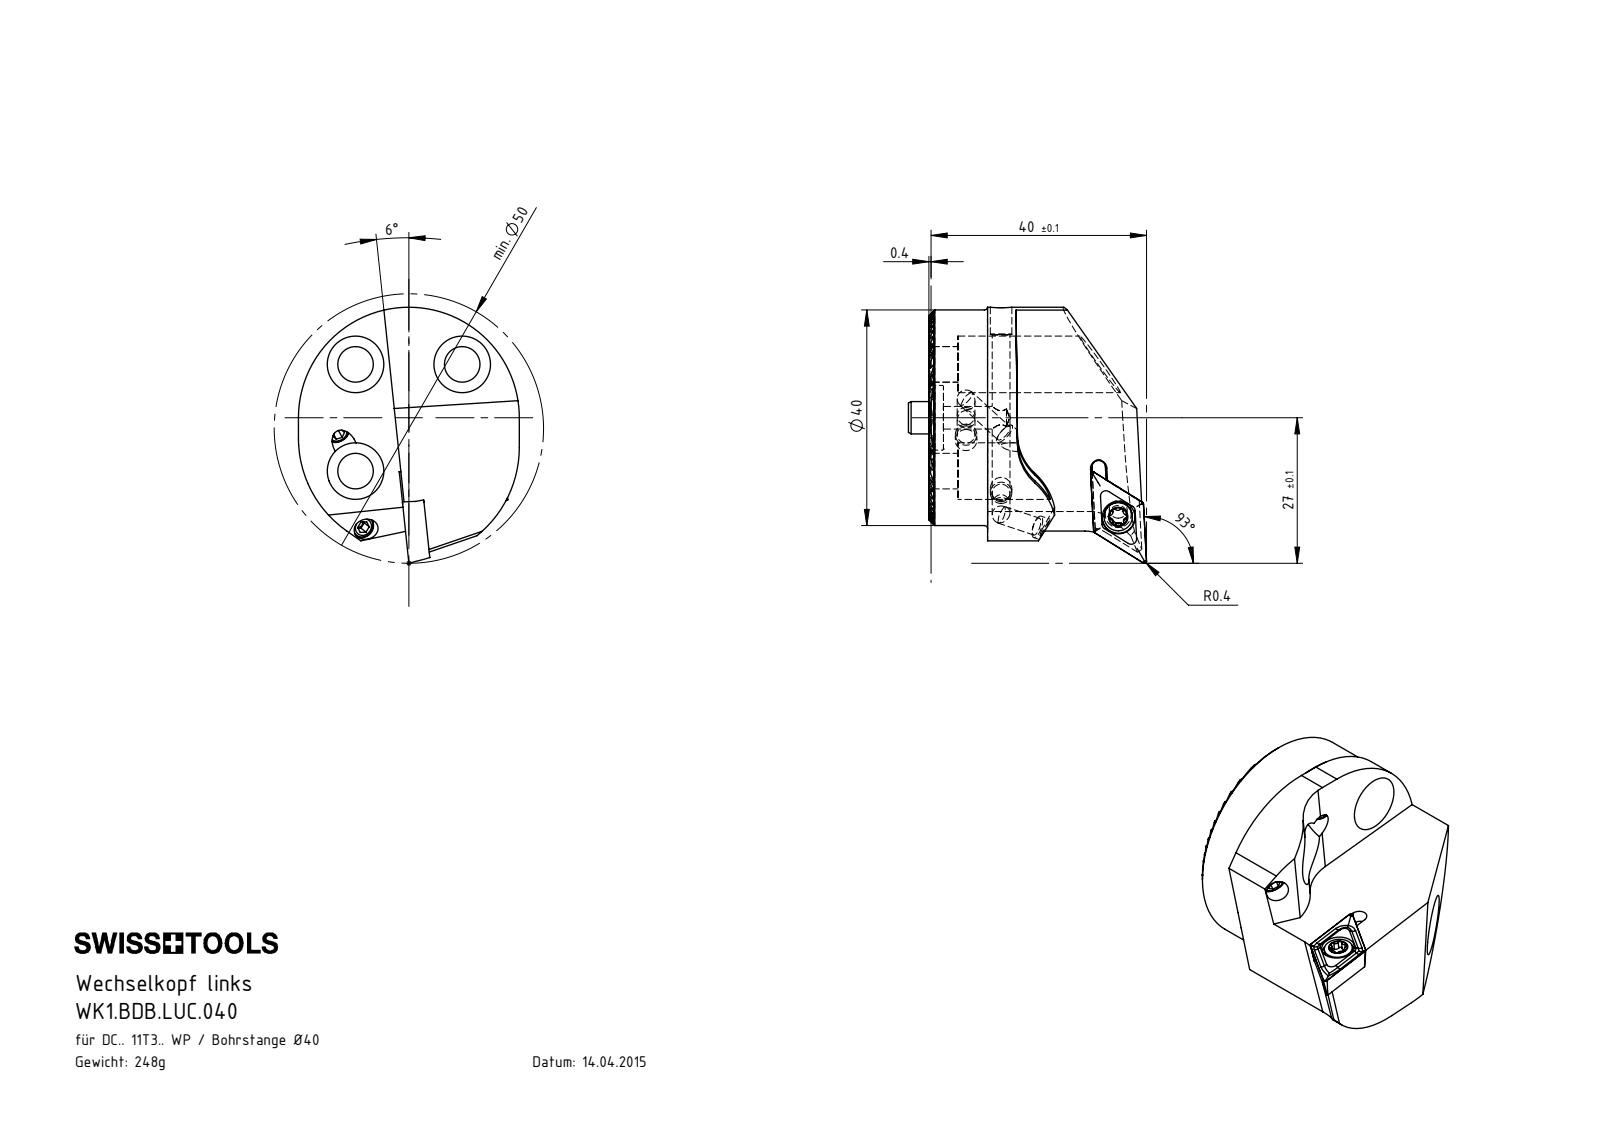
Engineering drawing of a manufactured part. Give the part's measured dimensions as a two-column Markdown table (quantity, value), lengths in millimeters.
| quantity | value |
| --- | --- |
| part name | DCMT11T304; WK1.BDB.LUC.040; KVT_MB_600_040; WK2-ER1.001.012_A_Fertigbearbeitung (+2 more) |
| STEP written by | SolidWorks 2017 (CONFIG_CONTROL_DESIGN) |
| units | millimeters |
| bodies | 11 solids, 407 faces (217 planar, 97 cylindrical, 93 other) |
| overall size | 47.51 × 44.2 × 41 |
| volume | 31 257 mm³ |
| surface area | 12 402 mm² |
| round holes (diameter × count) | 3.3 × 6, 3 × 3, 4.2 × 3, 6.6 × 3, 10.5 × 3, 1.7 × 2, 4 × 1, 4.4 × 1, 6.1 × 1, 12 × 1 |
| round bosses / shafts (diameter × count) | 4 × 5, 40 × 1, 6 × 1 |
| partial cylindrical surfaces (radius × count) | 0.12 × 26, 21 × 2, 1.25 × 1, 7 × 1, 10 × 1, 12 × 1, 20.5 × 1 |
| main face-to-face distances | 1.3, 2.6, 3.9, 12.99, 5.2, 11.69, 9.09, 10.39, 7.79, 6.5 |
| hole center spacings | 14, 19.8, 28 |
